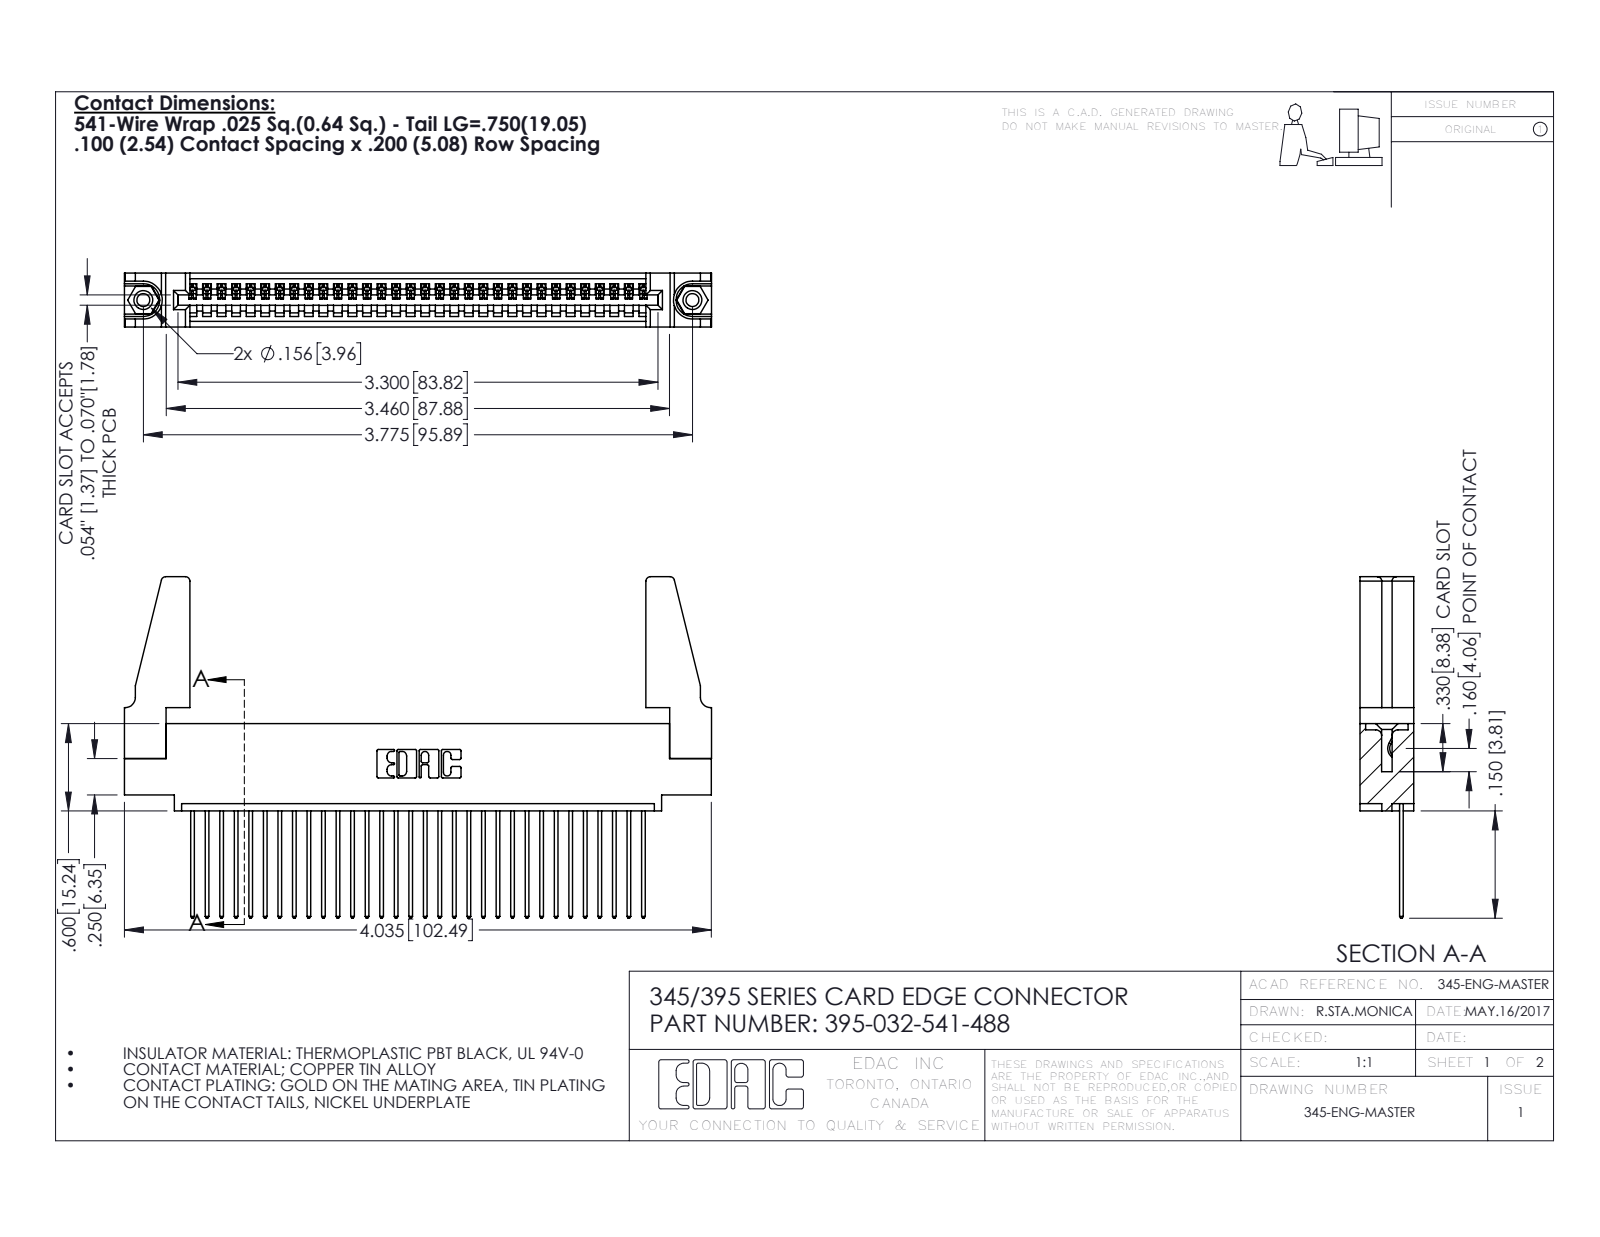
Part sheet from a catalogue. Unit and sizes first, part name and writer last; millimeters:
Units: millimetres
Overall size (bounding box): 102.5 × 59.6 × 9.4
Round holes (diameter × count): ⌀2.3 ×2, ⌀3.2 ×2, ⌀4 ×2, ⌀1.6 ×1
Round bosses / shafts (diameter × count): ⌀3.9 ×2
Partial cylindrical surfaces — rounded edges, fillets, slot ends (radius × count): R0.2 ×64, R0.3 ×64, R0.3 ×22, R0.8 ×8, R0.2 ×6, R0.8 ×6, R0.7 ×3, R0.8 ×2
Main face-to-face distances: 1.8, 7.6, 9.4, 2.5, 6.9, 0.6, 5.1, 5.7, 3.8, 1.8
Hole centre spacings: 6.9, 89.9, 95.9
Volume: 12 900 mm³ · Surface area: 16 570 mm²
Bodies: 37 solids, 2110 faces (1436 planar, 658 cylindrical, 16 other)
Part name (STEP PRODUCT): 395-032-541-488; 345-220-078_345-220-088; 345-292-001_345-293-141; 345-250-001_345-250-001-102 (+1 more)
STEP written by: SolidWorks 2016 (CONFIG_CONTROL_DESIGN)
